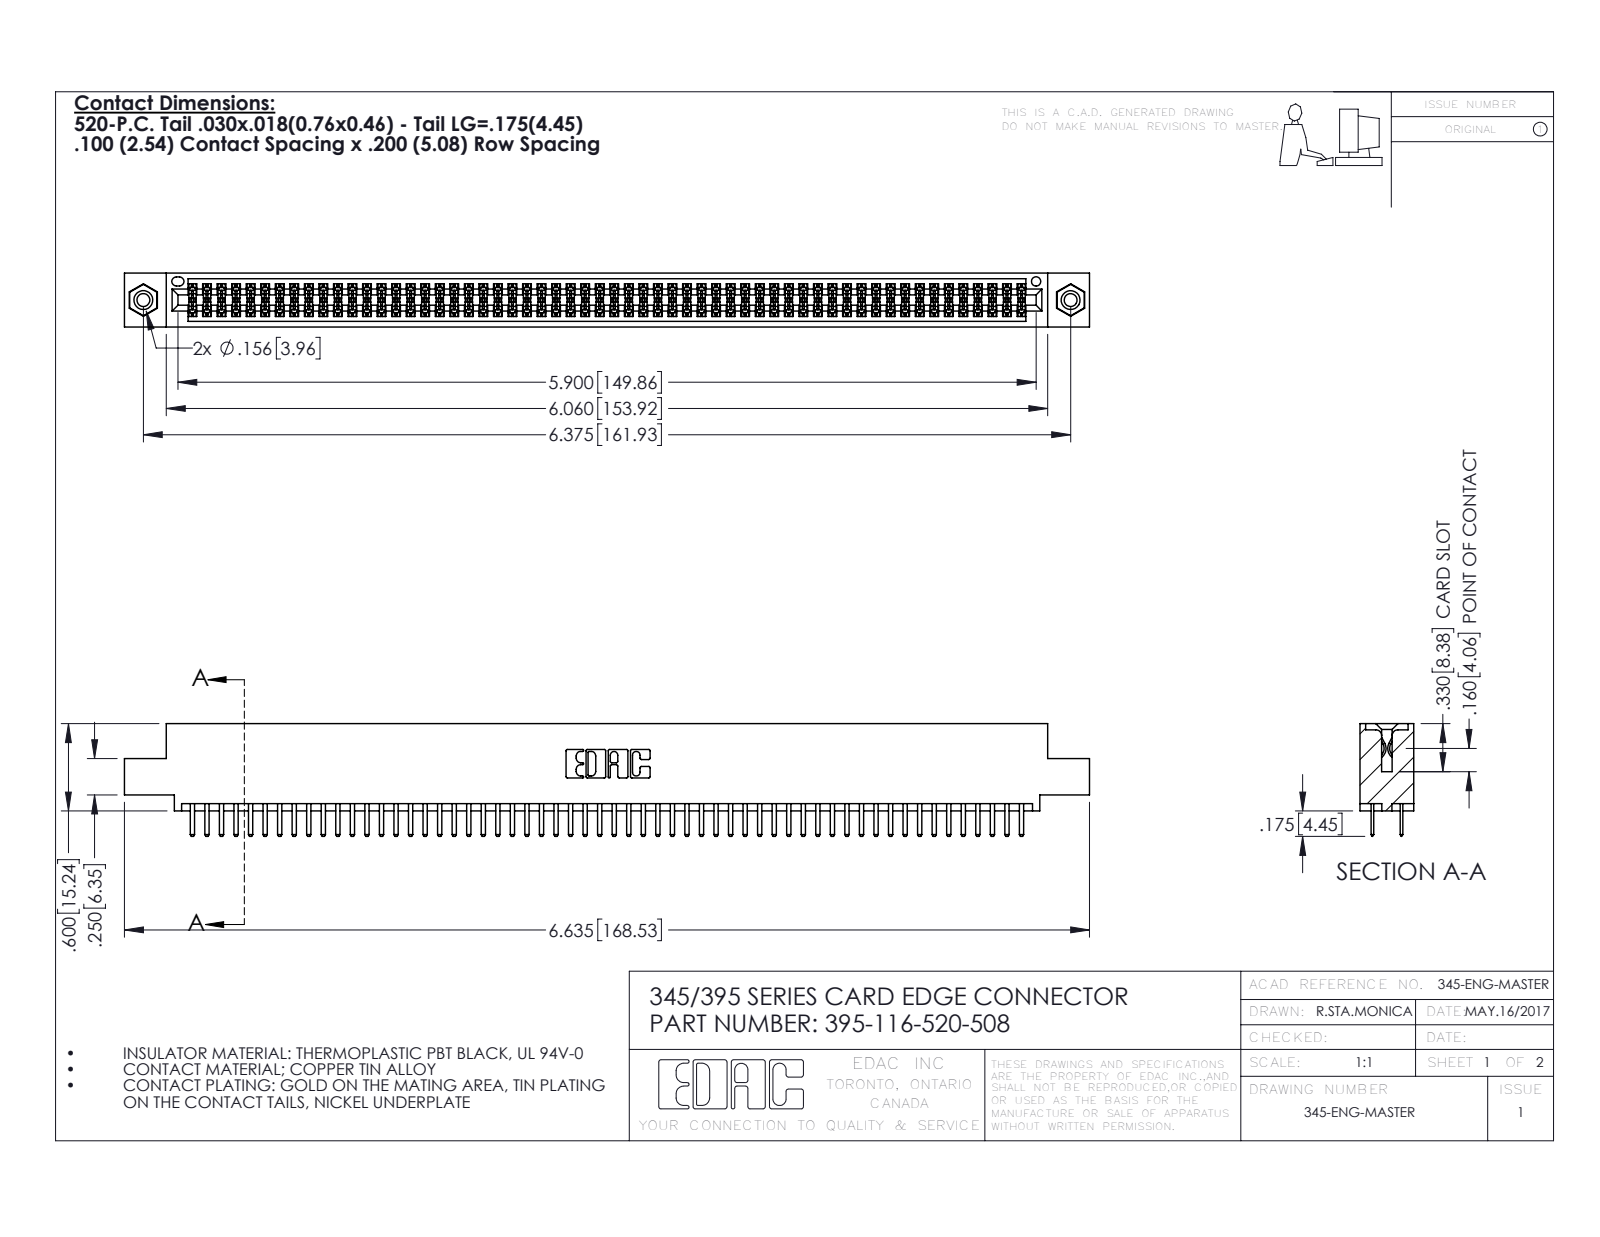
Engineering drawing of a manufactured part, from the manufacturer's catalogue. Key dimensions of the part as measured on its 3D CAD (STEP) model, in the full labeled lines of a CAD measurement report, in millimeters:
Part name (STEP PRODUCT): 345-250-001_345-250-003-102; 395-116-520-508; 345 Part_0.110 Offset - 0.156 Dia-TI; 345-292-001_345-293-120
STEP written by: SolidWorks 2016 (CONFIG_CONTROL_DESIGN)
Units: millimetres
Bodies: 119 solids, 6454 faces (4176 planar, 2262 cylindrical, 16 other)
Overall size (bounding box): 168.5 × 19.7 × 9.4
Volume: 16 390 mm³ · Surface area: 24 540 mm²
Round holes (diameter × count): ⌀2.3 ×2, ⌀3.2 ×2, ⌀4 ×2, ⌀1.6 ×1
Round bosses / shafts (diameter × count): ⌀3.9 ×2
Partial cylindrical surfaces — rounded edges, fillets, slot ends (radius × count): R0.2 ×174, R0.3 ×120, R0.3 ×22, R0.2 ×6, R0.8 ×6, R0.7 ×3, R0.4 ×2, R0.5 ×2
Main face-to-face distances: 1.8, 7.6, 5.1, 9.4, 2.5, 6.9, 0.6, 5.7, 0.6, 1.8
Hole centre spacings: 6.9, 155.9, 161.9
